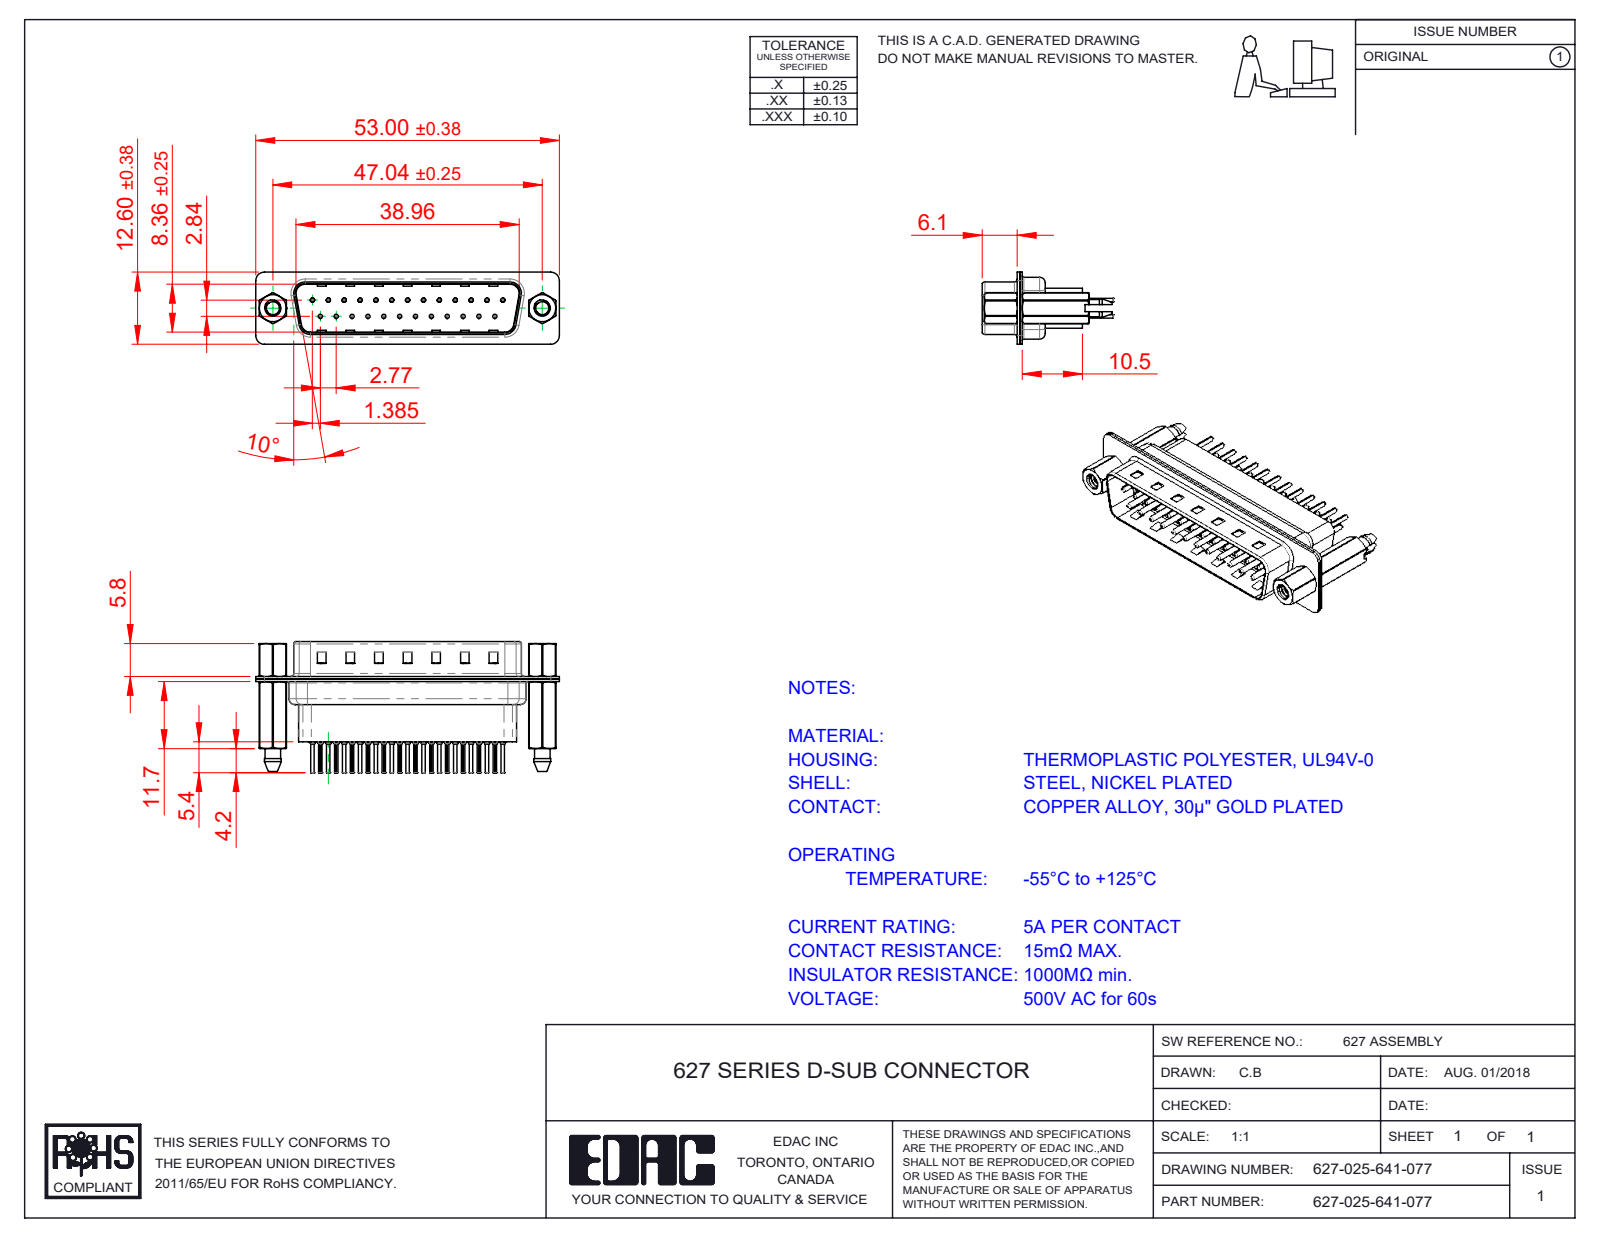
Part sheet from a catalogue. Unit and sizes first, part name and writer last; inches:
Units: inches
Overall size (bounding box): 2.087 × 0.898 × 0.496
Round holes (diameter × count): ⌀0.008 ×25, ⌀0.014 ×25, ⌀0.043 ×25, ⌀0.063 ×25, ⌀0.089 ×2, ⌀0.09 ×2, ⌀0.157 ×2, ⌀0.189 ×2
Round bosses / shafts (diameter × count): ⌀0.079 ×25, ⌀0.059 ×25, ⌀0.03 ×25, ⌀0.024 ×25, ⌀0.193 ×2, ⌀0.11 ×2
Partial cylindrical surfaces — rounded edges, fillets, slot ends (radius × count): R0.004 ×50, R0.059 ×18, R0.079 ×12, R0.063 ×10, R0.02 ×8, R0.01 ×4, R0.024 ×4, R0.026 ×4
Main face-to-face distances: 0.016, 0.018, 0.032, 0.377, 0.027, 0.302, 0.059, 0.035, 0.043, 0.318
Hole centre spacings: 0.124, 0.327, 0.109, 0.218, 0.436, 0.654, 0.198, 0.198
Volume: 0.263 in³ · Surface area: 17.09 in²
Bodies: 32 solids, 3060 faces (825 planar, 1200 cylindrical, 1035 other)
Part name (STEP PRODUCT): 627 4-40 Threaded Boardlock_HP41; 627 Housing_25 HP; 627 Shell Rear_25 Contacts; 627 Shell Front_25 Contacts (+4 more)
STEP written by: SolidWorks 2020 (CONFIG_CONTROL_DESIGN)
